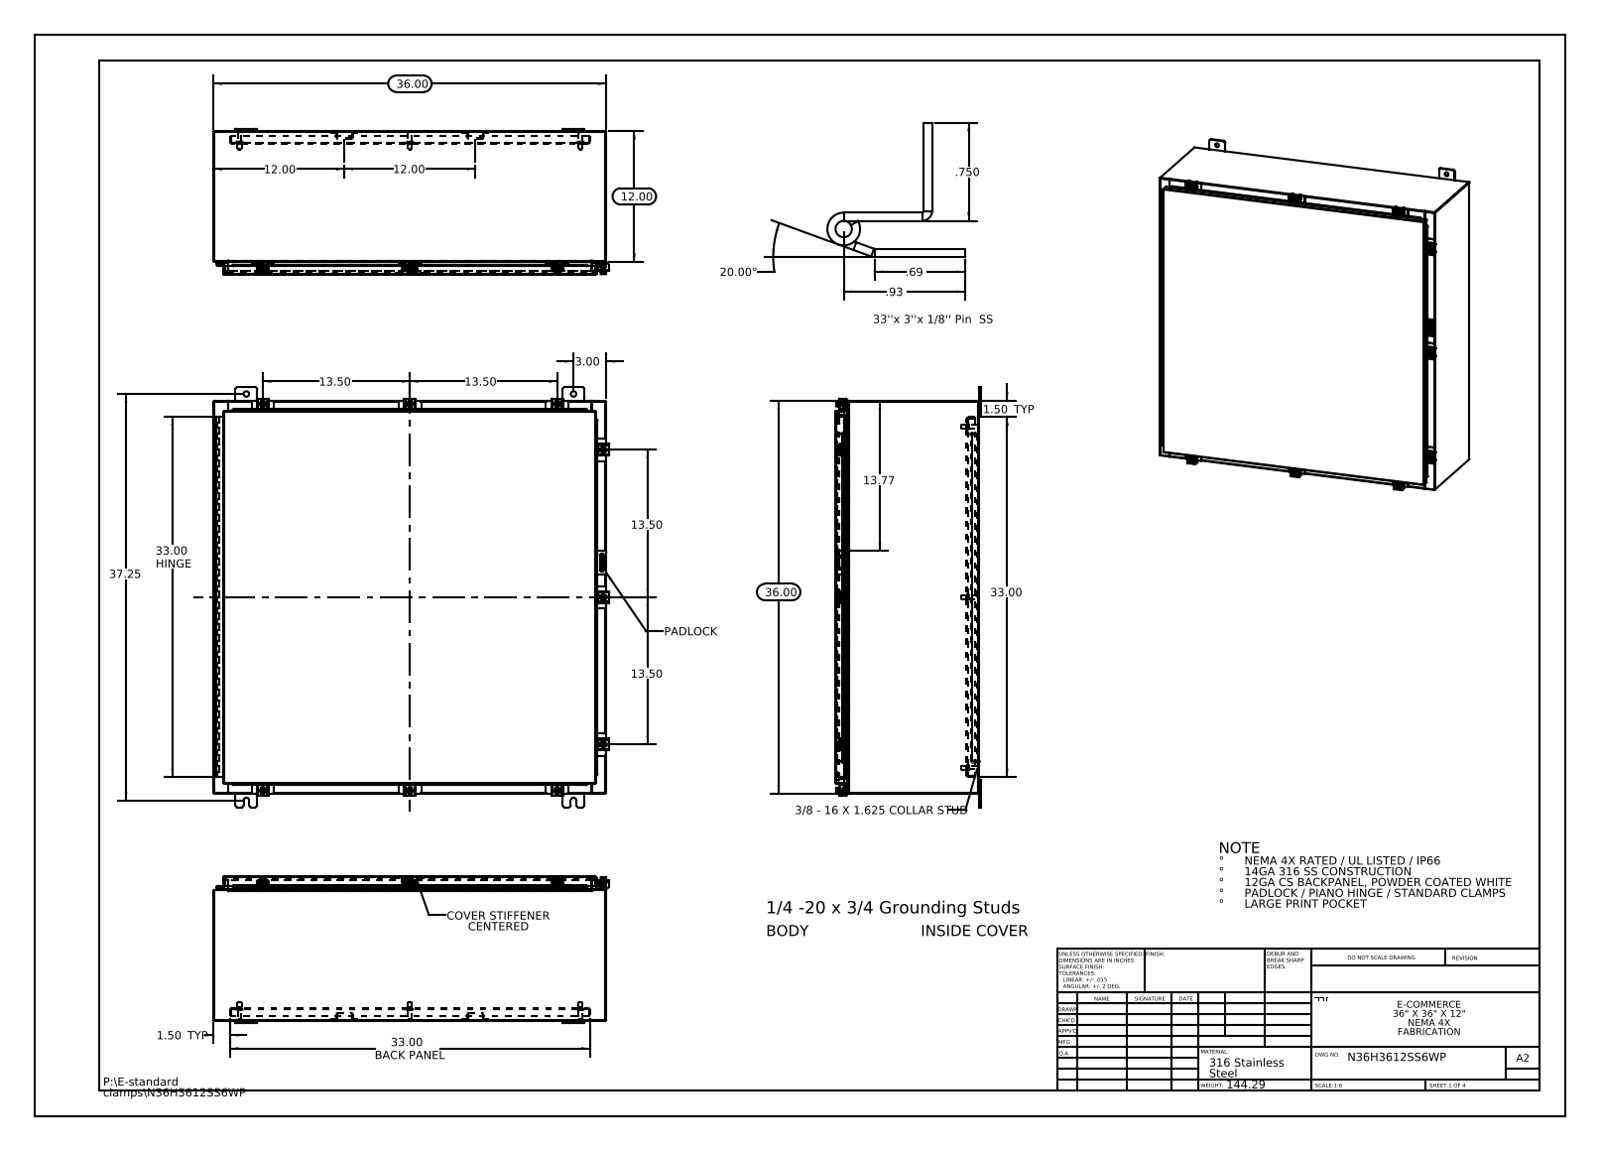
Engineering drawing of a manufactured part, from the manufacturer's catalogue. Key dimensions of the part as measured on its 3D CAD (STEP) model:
Part name (STEP PRODUCT): N36H3612SS6WP Standard Clamps; N36H3612SS6WP Hinge Enclosure Side2; N36H3612SS6WP Padlock Staple; N36H3612SS6WP Backpanel (+8 more)
STEP written by: SolidWorks 2013 (CONFIG_CONTROL_DESIGN)
Units: inches
Bodies: 69 solids, 2594 faces (1358 planar, 1076 cylindrical, 160 other)
Overall size (bounding box): 38.5 × 36.211 × 13.389
Volume: 505.6 in³ · Surface area: 12 667 in²
Round holes (diameter × count): ⌀0.5 ×12, ⌀0.213 ×9, ⌀0.26 ×9, ⌀0.25 ×6, ⌀0.125 ×2, ⌀0.125 ×1
Round bosses / shafts (diameter × count): ⌀0.25 ×10, ⌀0.5 ×9, ⌀0.399 ×9, ⌀0.625 ×8, ⌀0.375 ×8, ⌀0.33 ×8
Partial cylindrical surfaces — rounded edges, fillets, slot ends (radius × count): R0.06 ×42, R0.013 ×39, R0.088 ×33, R0.19 ×24, R0.12 ×18, R0.141 ×18, R0.05 ×13, R0.08 ×12
Main face-to-face distances: 0.075, 13.126, 35.925, 13.051, 13.201, 0.104, 1, 12.126, 1.075, 12.051
Hole centre spacings: 13.5, 13.663, 15.625, 17.852, 23.629, 33.419, 34.095, 35.98
